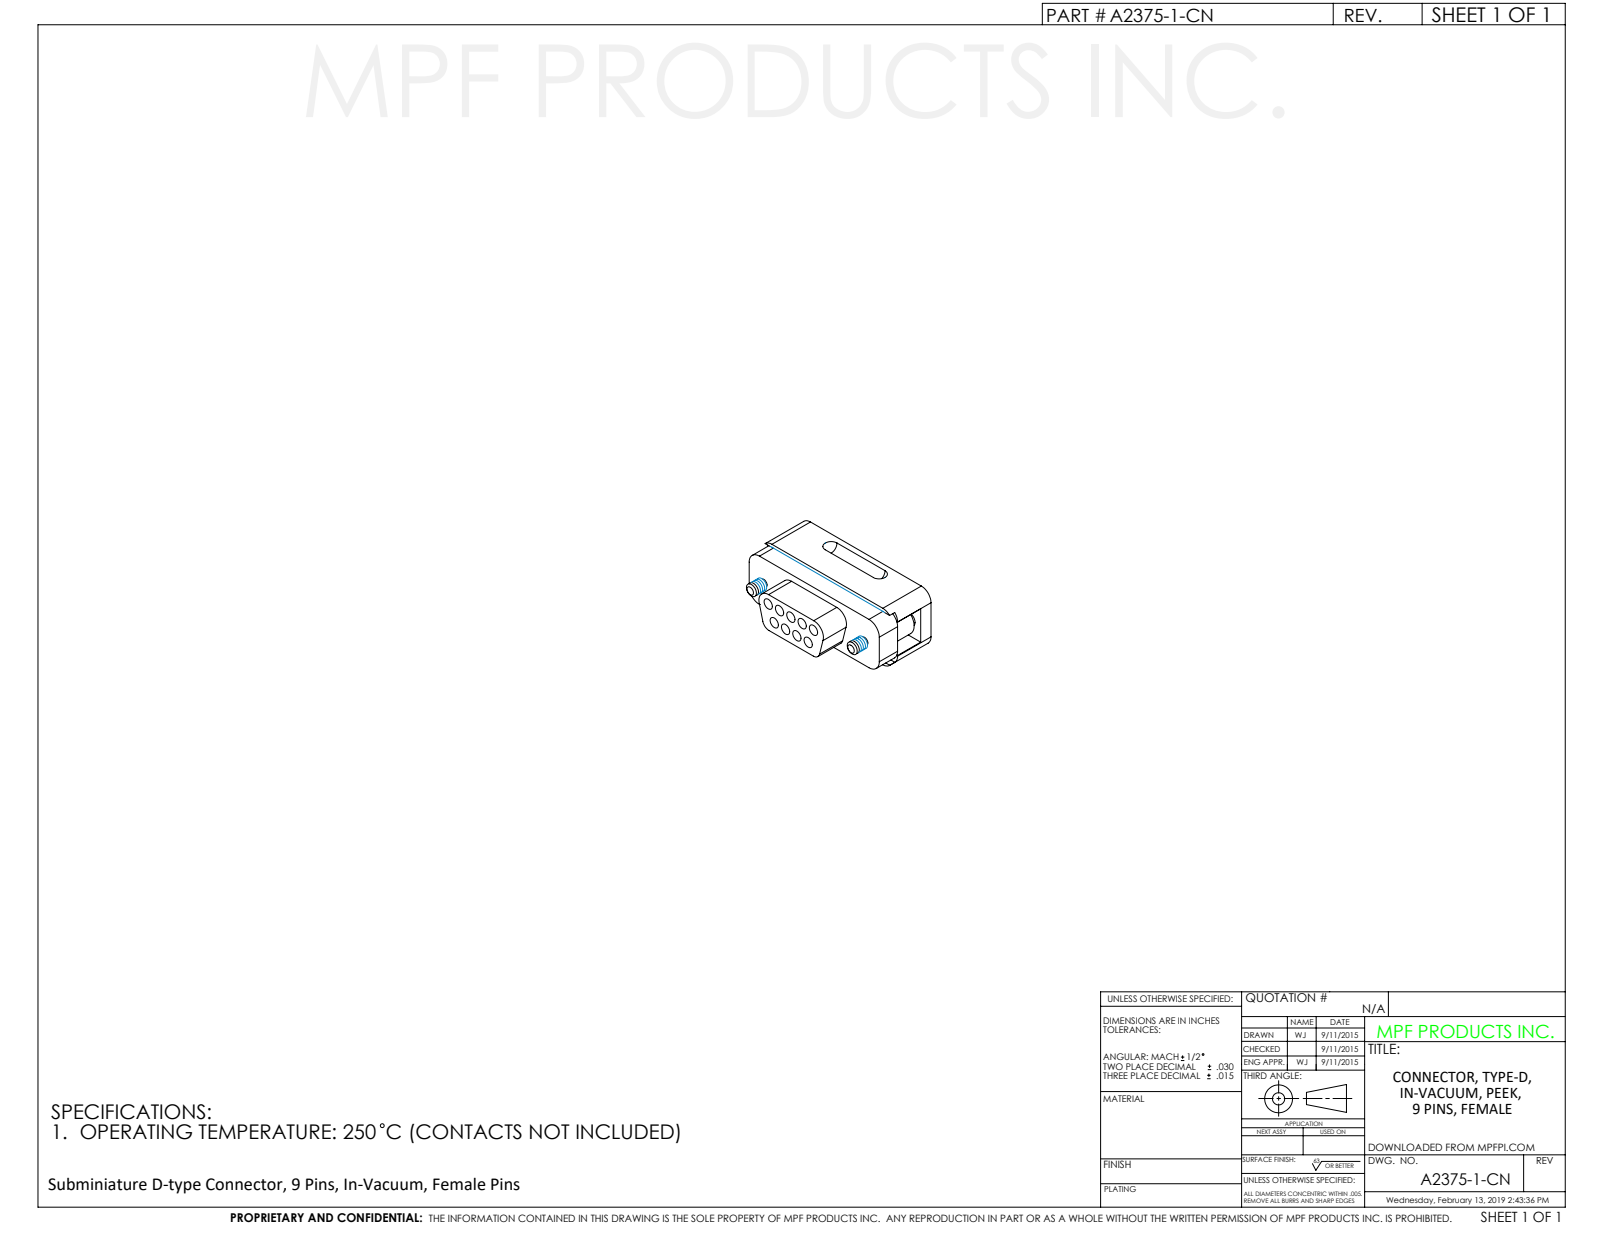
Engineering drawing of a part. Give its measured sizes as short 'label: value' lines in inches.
name: A2375-1-CN
written by: SolidWorks 2012 (CONFIG_CONTROL_DESIGN)
unit: in
bodies: 0 solids, 118 faces (35 planar, 47 cylindrical, 36 other)
size: 1.265 × 0.727 × 0.475
holes: 9× ⌀0.08, 2× ⌀0.11
bosses: 2× ⌀0.063
rounds: 6× R0.094, 4× R0.1, 2× R0.057, 2× R0.063, 2× R0.113
face distances: 0.475, 0.503, 0.036, 0.443, 0.407, 0.439, 0.032, 0.375, 0.727, 0.224
hole spacings: 0.11, 0.138, 0.22, 0.11, 0.141, 0.206, 0.211, 0.33
